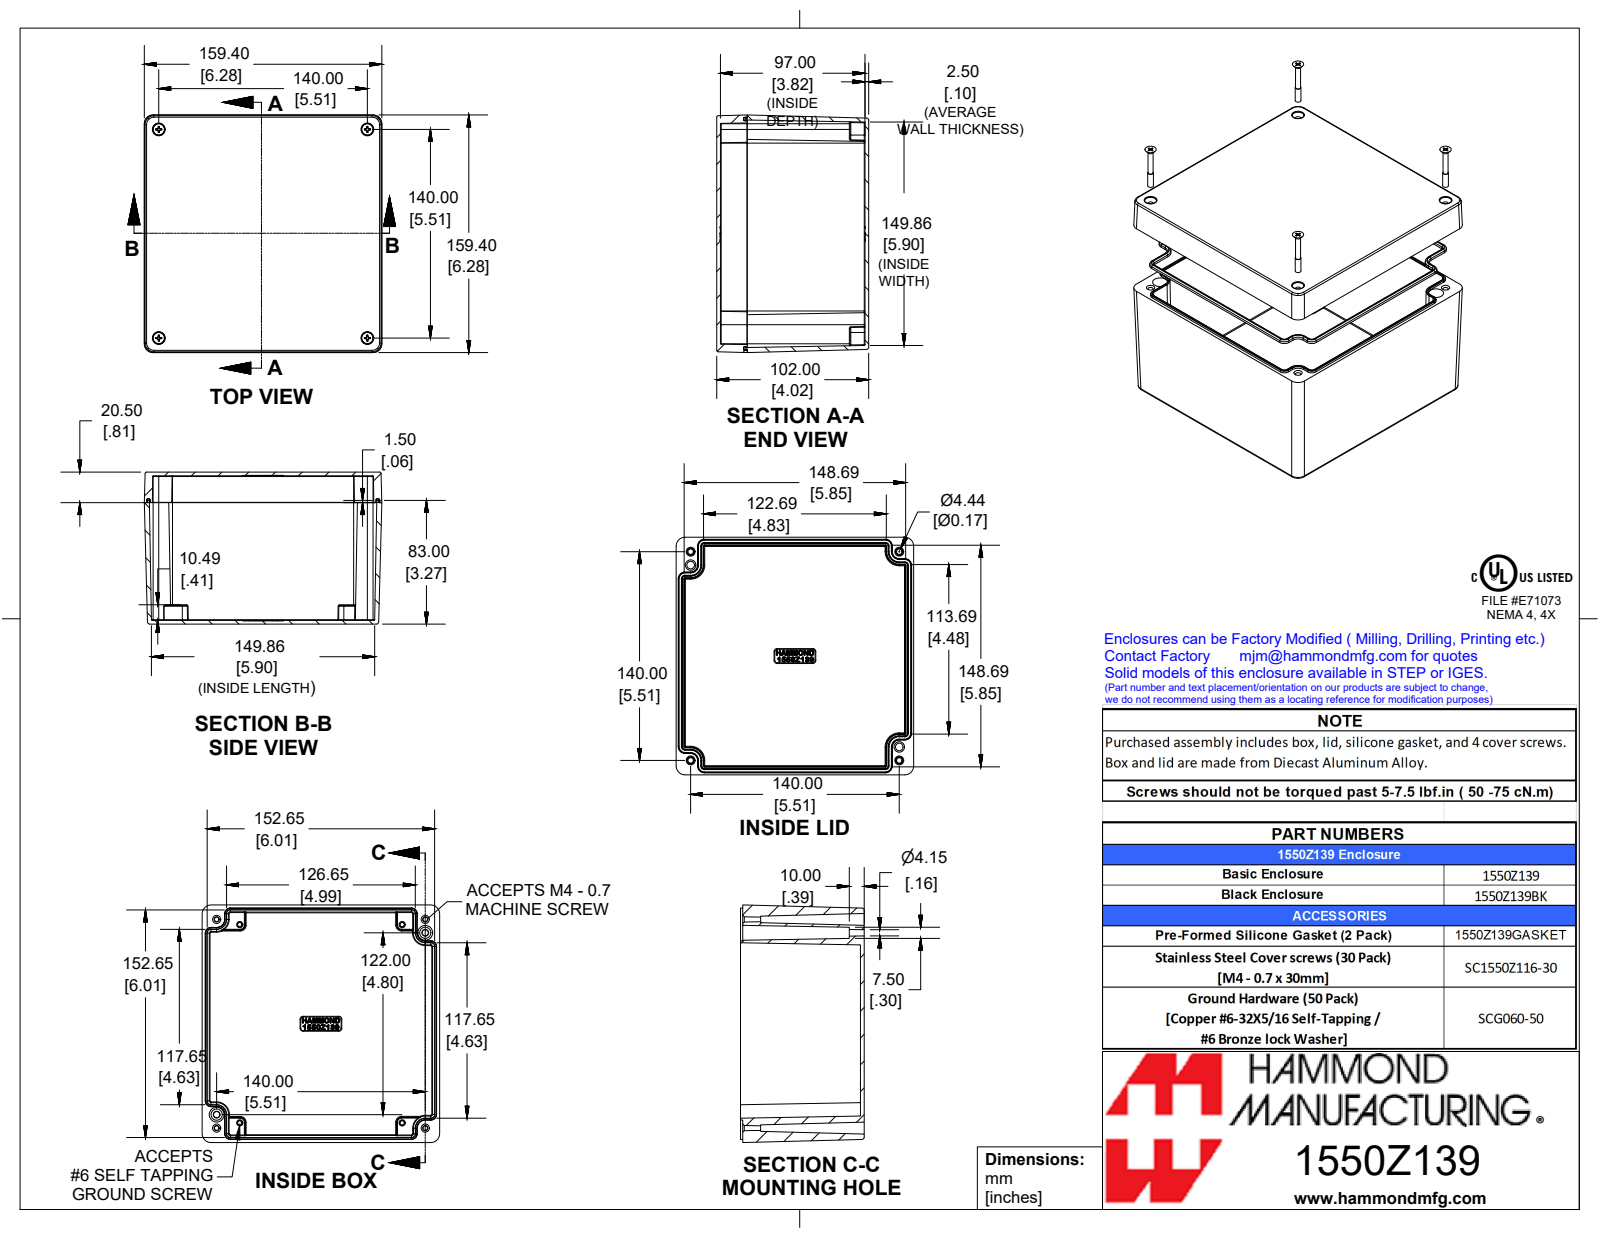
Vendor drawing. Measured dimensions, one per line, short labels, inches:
name: 1550Z139
written by: SolidWorks 2019 (AUTOMOTIVE_DESIGN)
unit: in
bodies: 7 solids, 1452 faces (381 planar, 256 cylindrical, 815 other)
size: 6.276 × 6.276 × 4.016
volume: 24.26 in³; area: 373.9 in²
holes: 4× ⌀0.142
bosses: 4× ⌀0.299, 4× ⌀0.154, 4× ⌀0.13
rounds: 50× R0.008, 48× R0.02, 24× R0.039, 20× R0.012, 8× R0.236, 4× R0.059
face distances: 0.098, 3.917, 4.016, 3.819, 6.276, 5.931, 3.209, 0.709, 3.11, 0.807
hole spacings: 5.512, 7.795
